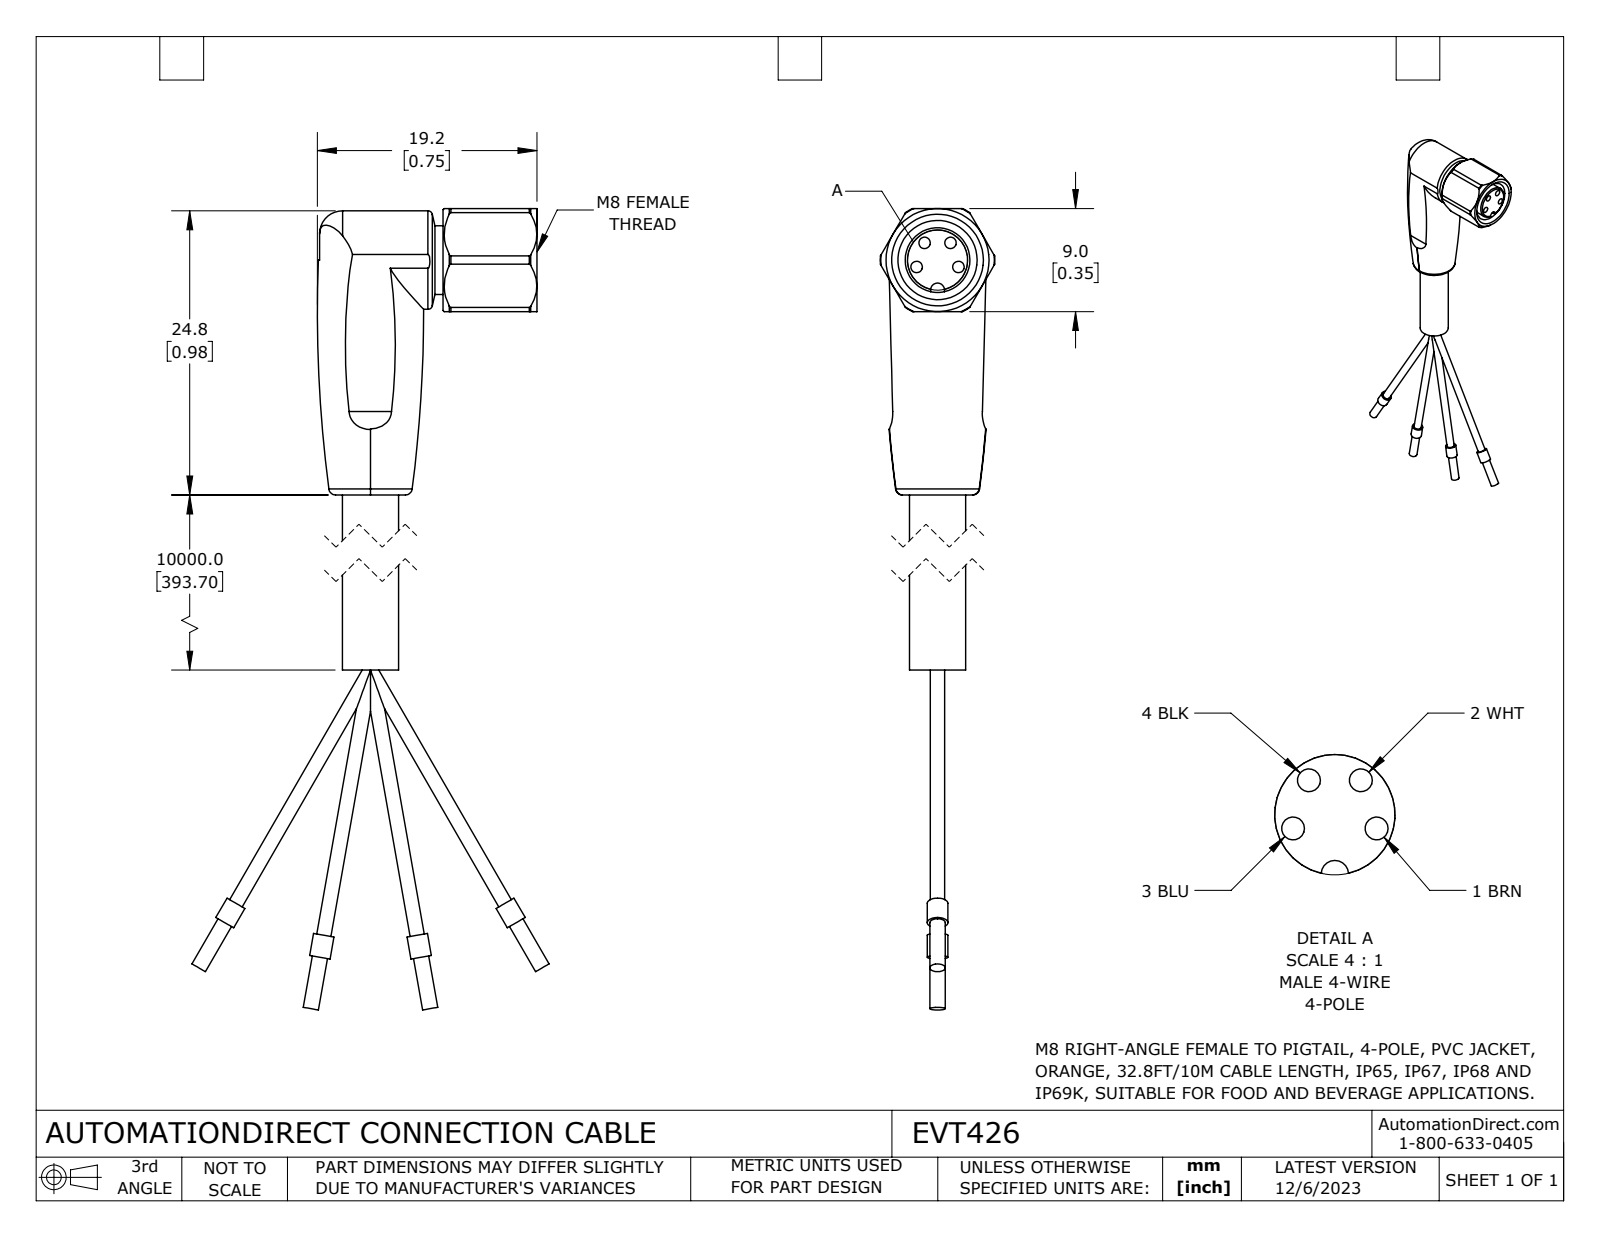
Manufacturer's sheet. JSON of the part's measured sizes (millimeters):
{"part_name": "EVT426", "step_written_by": "SolidWorks 2023 (CONFIG_CONTROL_DESIGN)", "units": "millimeters", "bodies": {"solids": 1, "faces": 122, "planar": 37, "cylindrical": 53, "other": 32}, "overall_size": [68.2, 31.2, 10], "volume_mm3": 2410, "surface_area_mm2": 2103, "round_holes": [[1, 4], [6.9, 1]], "round_bosses_or_shafts": [[1.8, 4], [1.3, 4], [1.2, 4], [8.6, 1], [6, 1], [5.6, 1], [4.9, 1]], "partial_cylinders_radius": [[3.2, 2], [0.6, 1], [5, 1]], "face_to_face_distances": [9, 8.2, 29.5, 38.5, 2.5, 5.7, 13.5, 16, 25, 2], "hole_center_spacings": [1.9, 1.9, 2.2, 3.6, 2.3, 3.6]}
